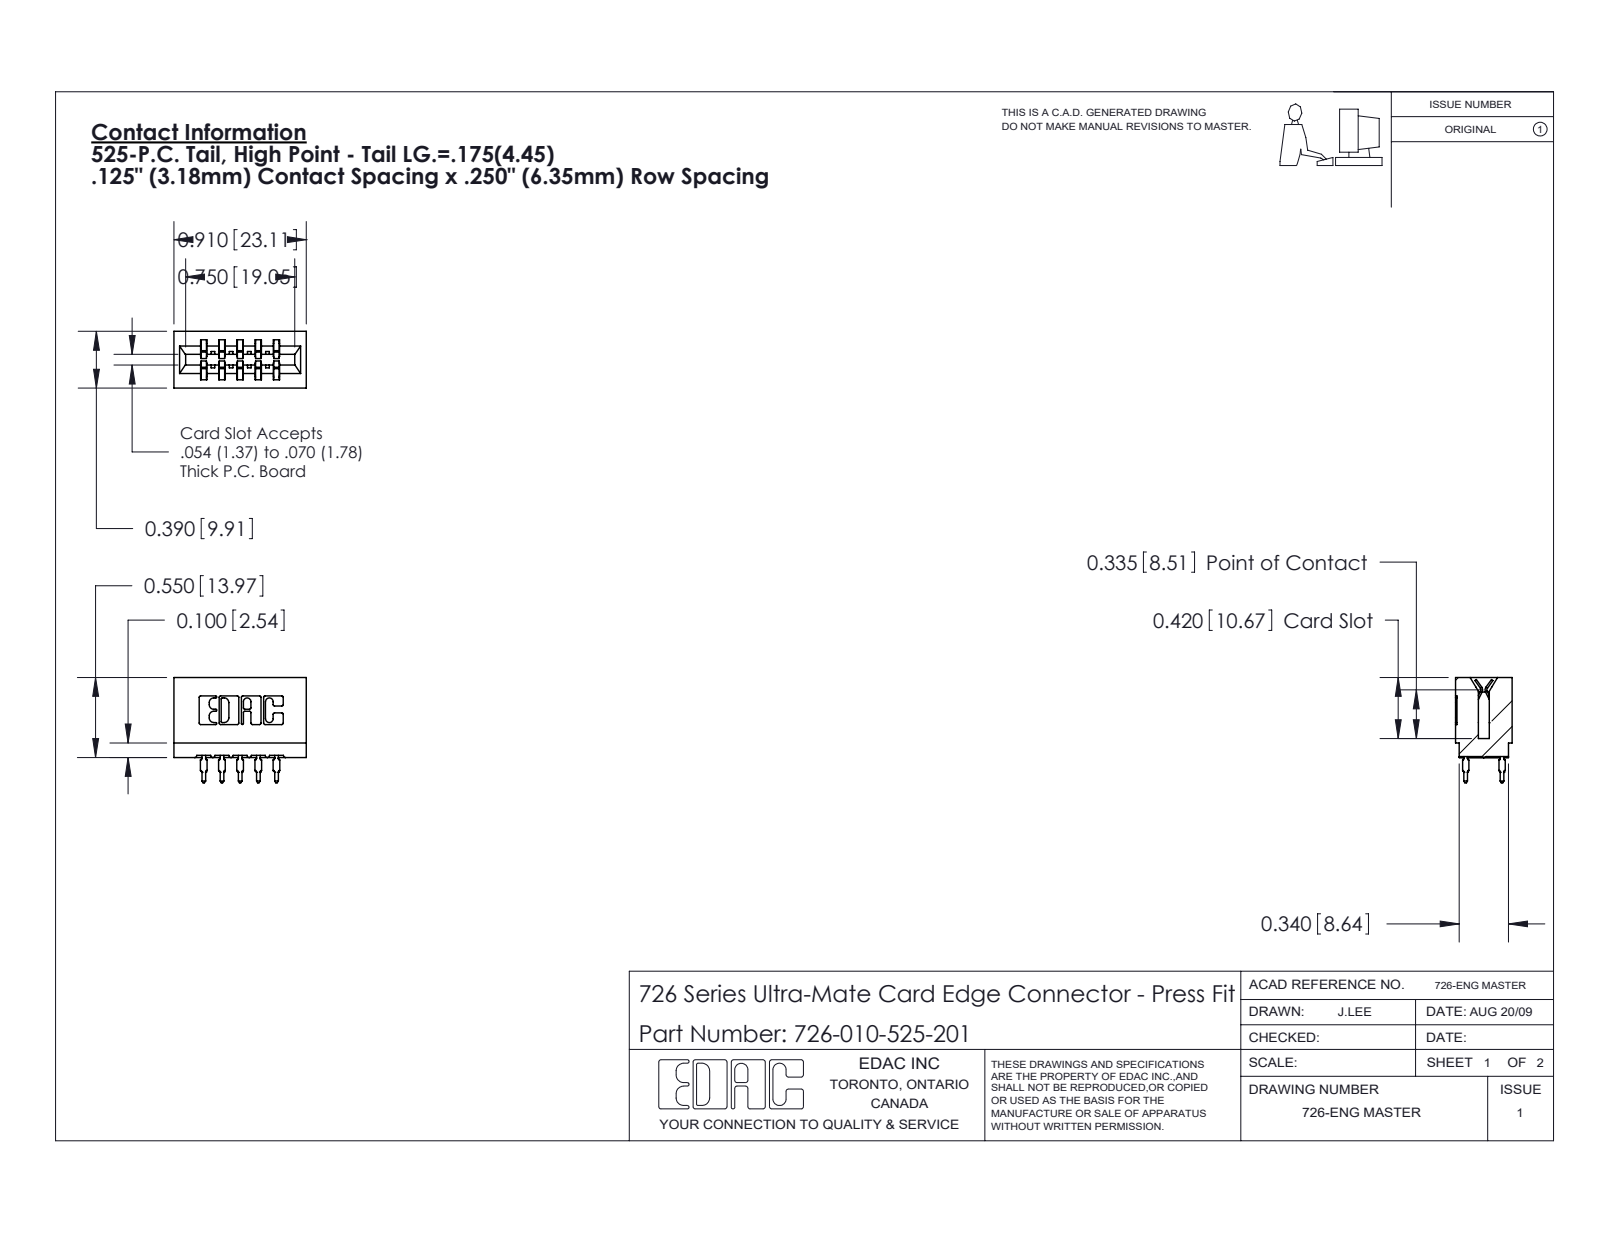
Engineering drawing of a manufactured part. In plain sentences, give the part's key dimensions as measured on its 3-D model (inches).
The part is named "726 Part_.515 Slot Depth - 01; 726-010-525-201; 746-292-001_525". Its 3-D file was written by "SolidWorks 2020 (CONFIG_CONTROL_DESIGN)". It is 11 solids with 992 faces: 515 planar, 217 cylindrical and 260 other. Overall it measures 0.91 by 0.724 by 0.39 inches. Its volume is 0.141 cubic inches and its surface area 4.934 square inches. Partial cylindrical surfaces (rounded edges, fillets, slot ends): 22 of radius 0.01, 20 of radius 0.021, 8 of radius 0.005, 8 of radius 0.011, 6 of radius 0.007, 6 of radius 0.015, 6 of radius 0.031, 3 of radius 0.026. The main face-to-face distances are 0.25, 0.042, 0.057, 0.333, 0.125, 0.125, 0.39, 0.083, 0.025, 0.292.
